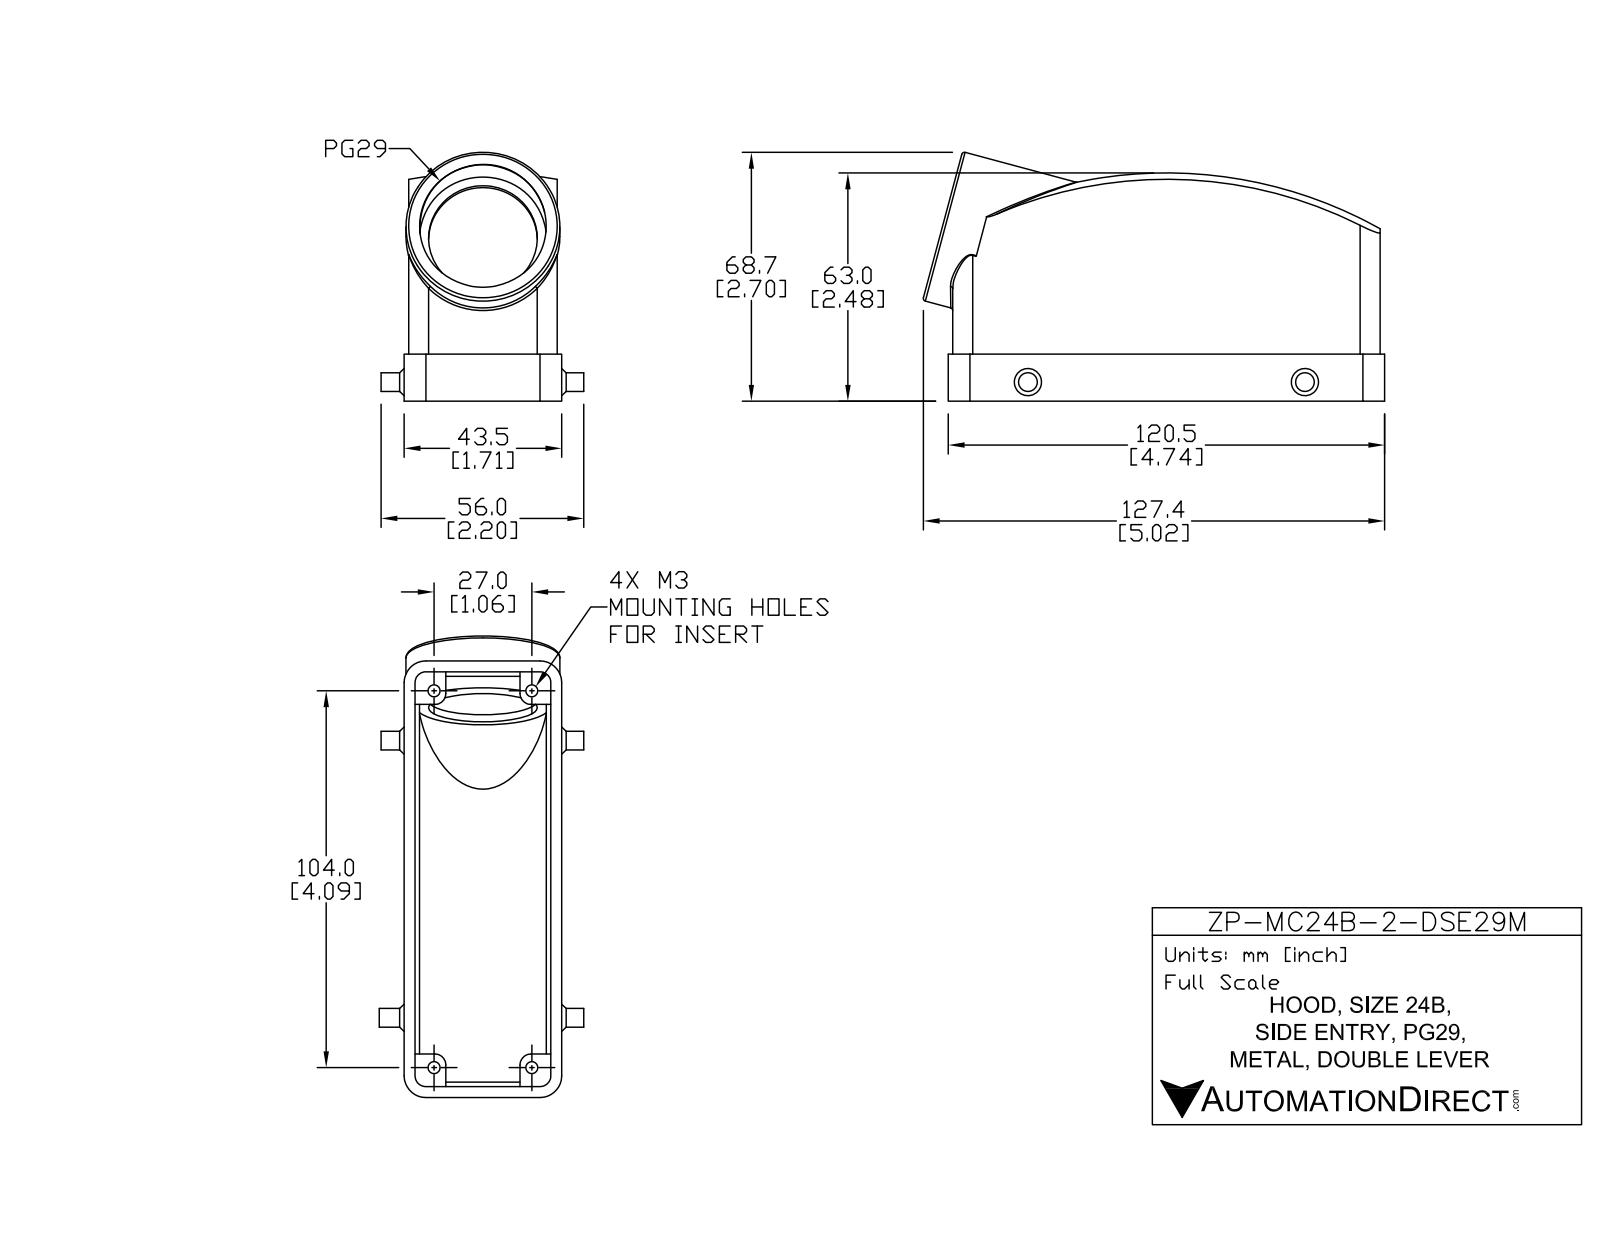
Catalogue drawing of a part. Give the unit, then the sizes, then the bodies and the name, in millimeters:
Units: millimetres
Overall size (bounding box): 127.4 × 68.71 × 56
Round holes (diameter × count): ⌀3.3 ×4, ⌀30 ×1, ⌀35 ×1
Round bosses / shafts (diameter × count): ⌀5.17 ×2, ⌀42.5 ×1
Partial cylindrical surfaces — rounded edges, fillets, slot ends (radius × count): R3 ×8, R5.5 ×4, R6 ×4, R0.75 ×2, R18.25 ×1
Main face-to-face distances: 3, 38, 1.25, 39.25, 41, 35, 4.25, 42.25, 1.75, 40.5
Hole centre spacings: 27, 104, 107.45
Volume: 72 657 mm³ · Surface area: 45 673 mm²
Bodies: 5 solids, 96 faces (54 planar, 31 cylindrical, 11 other)
Part name (STEP PRODUCT): ZP-MC24B-2-DSE29M
STEP written by: SolidWorks 2011 (AUTOMOTIVE_DESIGN)
